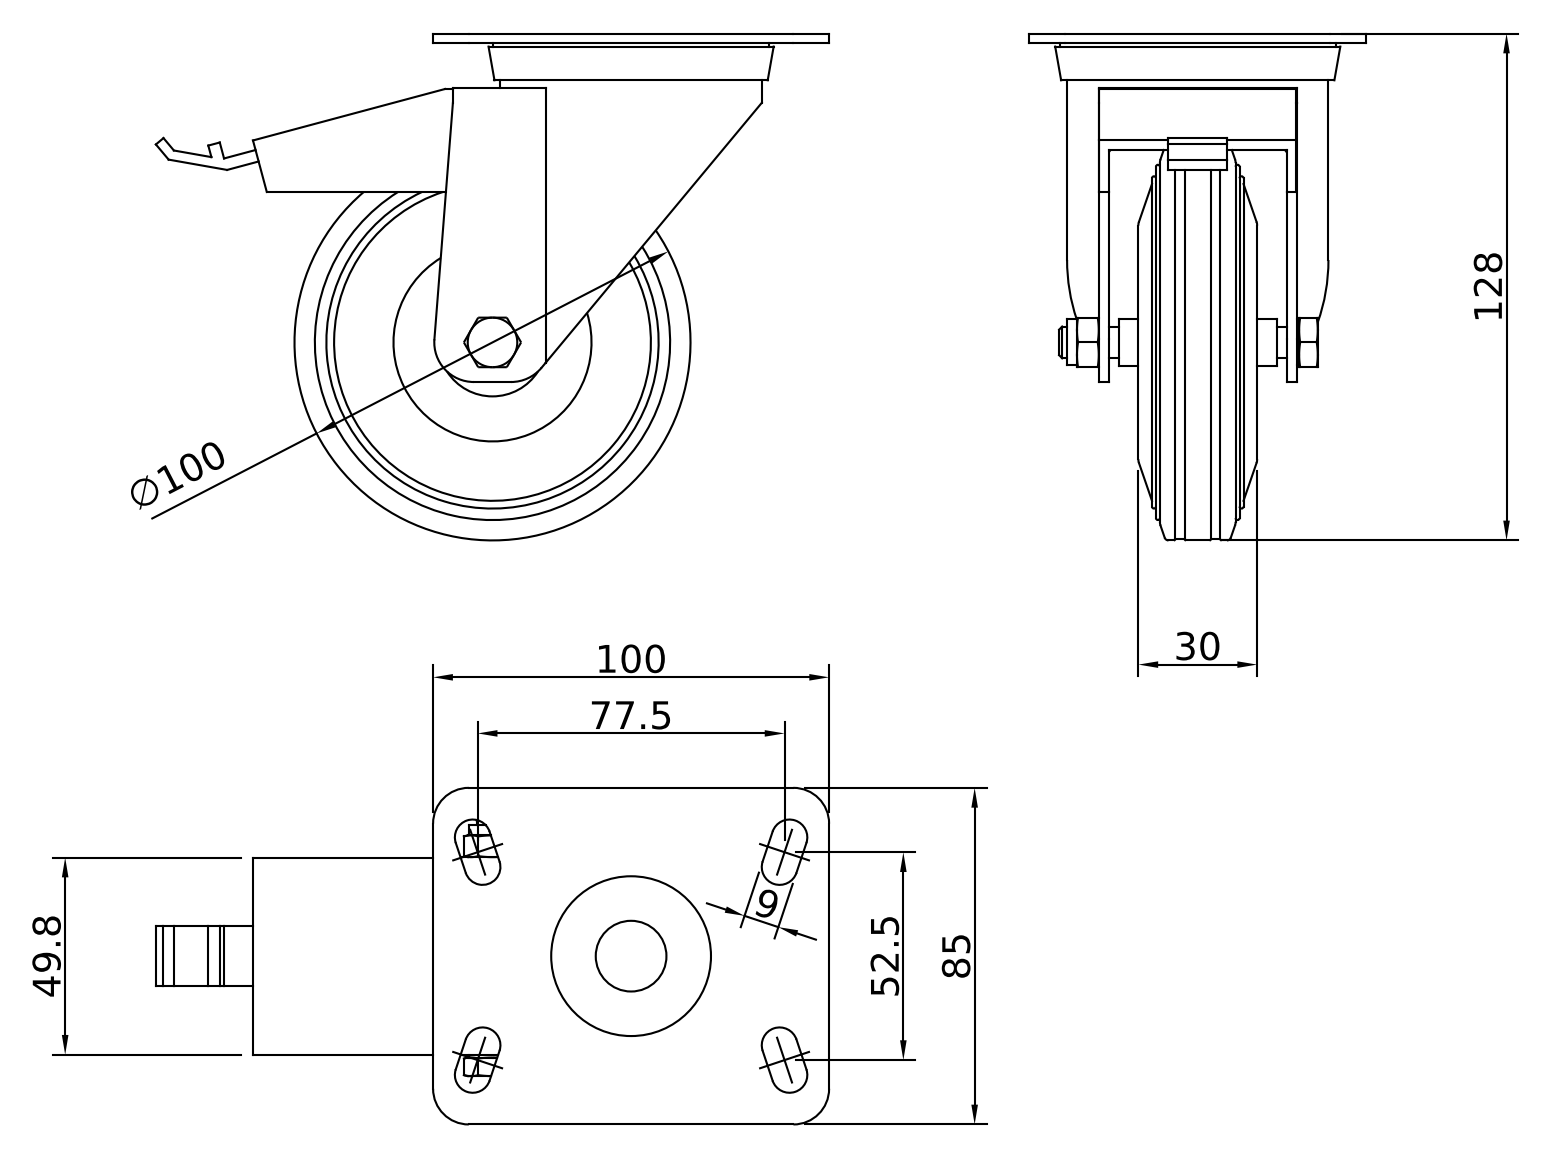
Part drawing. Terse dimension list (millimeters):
name: CRUST0000200; 440000025848; 440000025847; 440000025846
written by: Autodesk Inventor 2022 (AUTOMOTIVE_DESIGN)
unit: mm
bodies: 3 solids, 187 faces (89 planar, 34 cylindrical, 64 other)
size: 170 × 128 × 85
volume: 270 227 mm³; area: 79 576 mm²
holes: 1× ⌀12, 1× ⌀40.35, 1× ⌀61
bosses: 1× ⌀100, 1× ⌀99.4, 1× ⌀69.6, 1× ⌀66, 1× ⌀11.63, 1× ⌀8
rounds: 8× R4.5, 4× R9, 2× R10
face distances: 2.5, 47.5, 14, 11.5, 45, 7.5, 40, 37.5, 50, 10
hole spacings: 2
